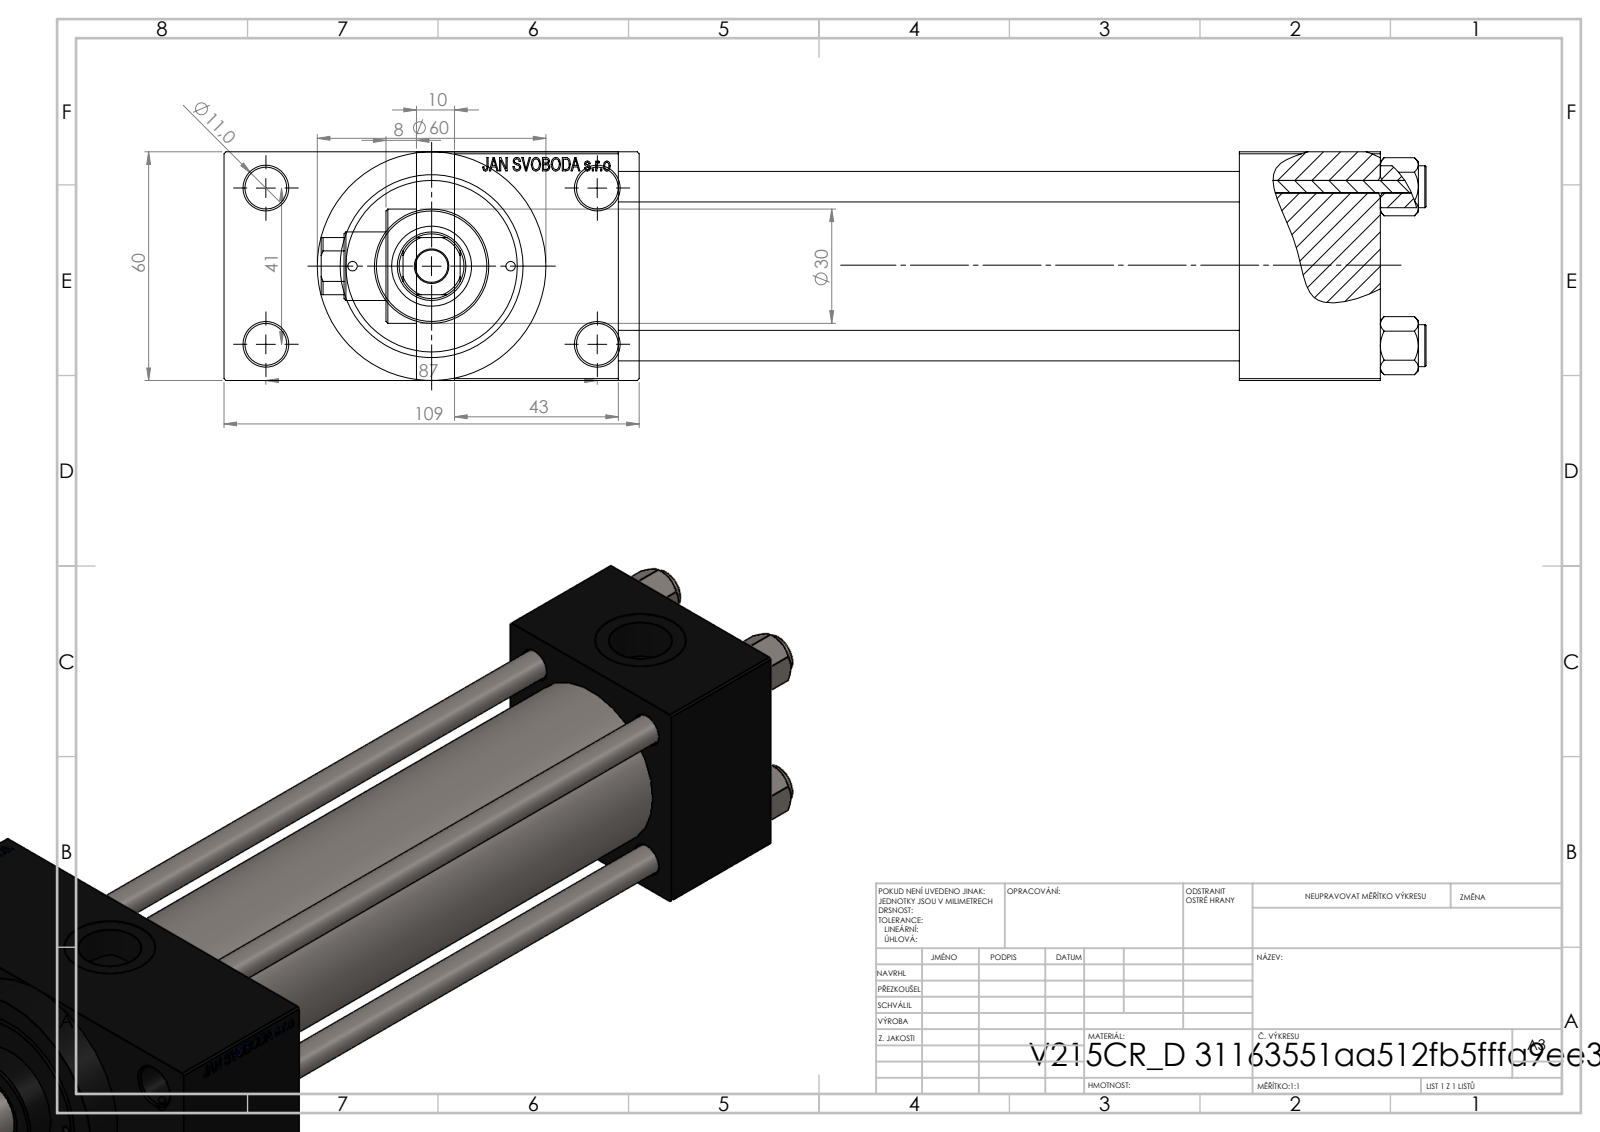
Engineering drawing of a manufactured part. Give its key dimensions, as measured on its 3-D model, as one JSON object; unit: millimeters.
{"part_name": "V215_VC_A; NUT_M5_D; V215CR_D_Body; V215CR_D_TYCINKA (+1 more)", "step_written_by": "SolidWorks 2019 (CONFIG_CONTROL_DESIGN)", "units": "millimeters", "bodies": {"solids": 11, "faces": 1113, "planar": 500, "cylindrical": 93, "other": 520}, "overall_size": [290, 109, 60], "volume_mm3": 607938, "surface_area_mm2": 166086, "round_holes": [[8, 4], [11, 4], [2.5, 2], [7, 2], [16.66, 2], [24, 2], [8.5, 1], [18, 1], [21, 1], [31, 1], [40, 1], [45, 1]], "round_bosses_or_shafts": [[11, 4], [60, 1], [46, 1], [30, 1]], "partial_cylinders_radius": [[8.5, 1]], "face_to_face_distances": [60, 24.5, 84.5, 163, 37, 200, 243, 206, 43, 109], "hole_center_spacings": [20.85, 22.65, 29.49, 30.62, 41.7, 46.53, 47.15, 48.09]}
